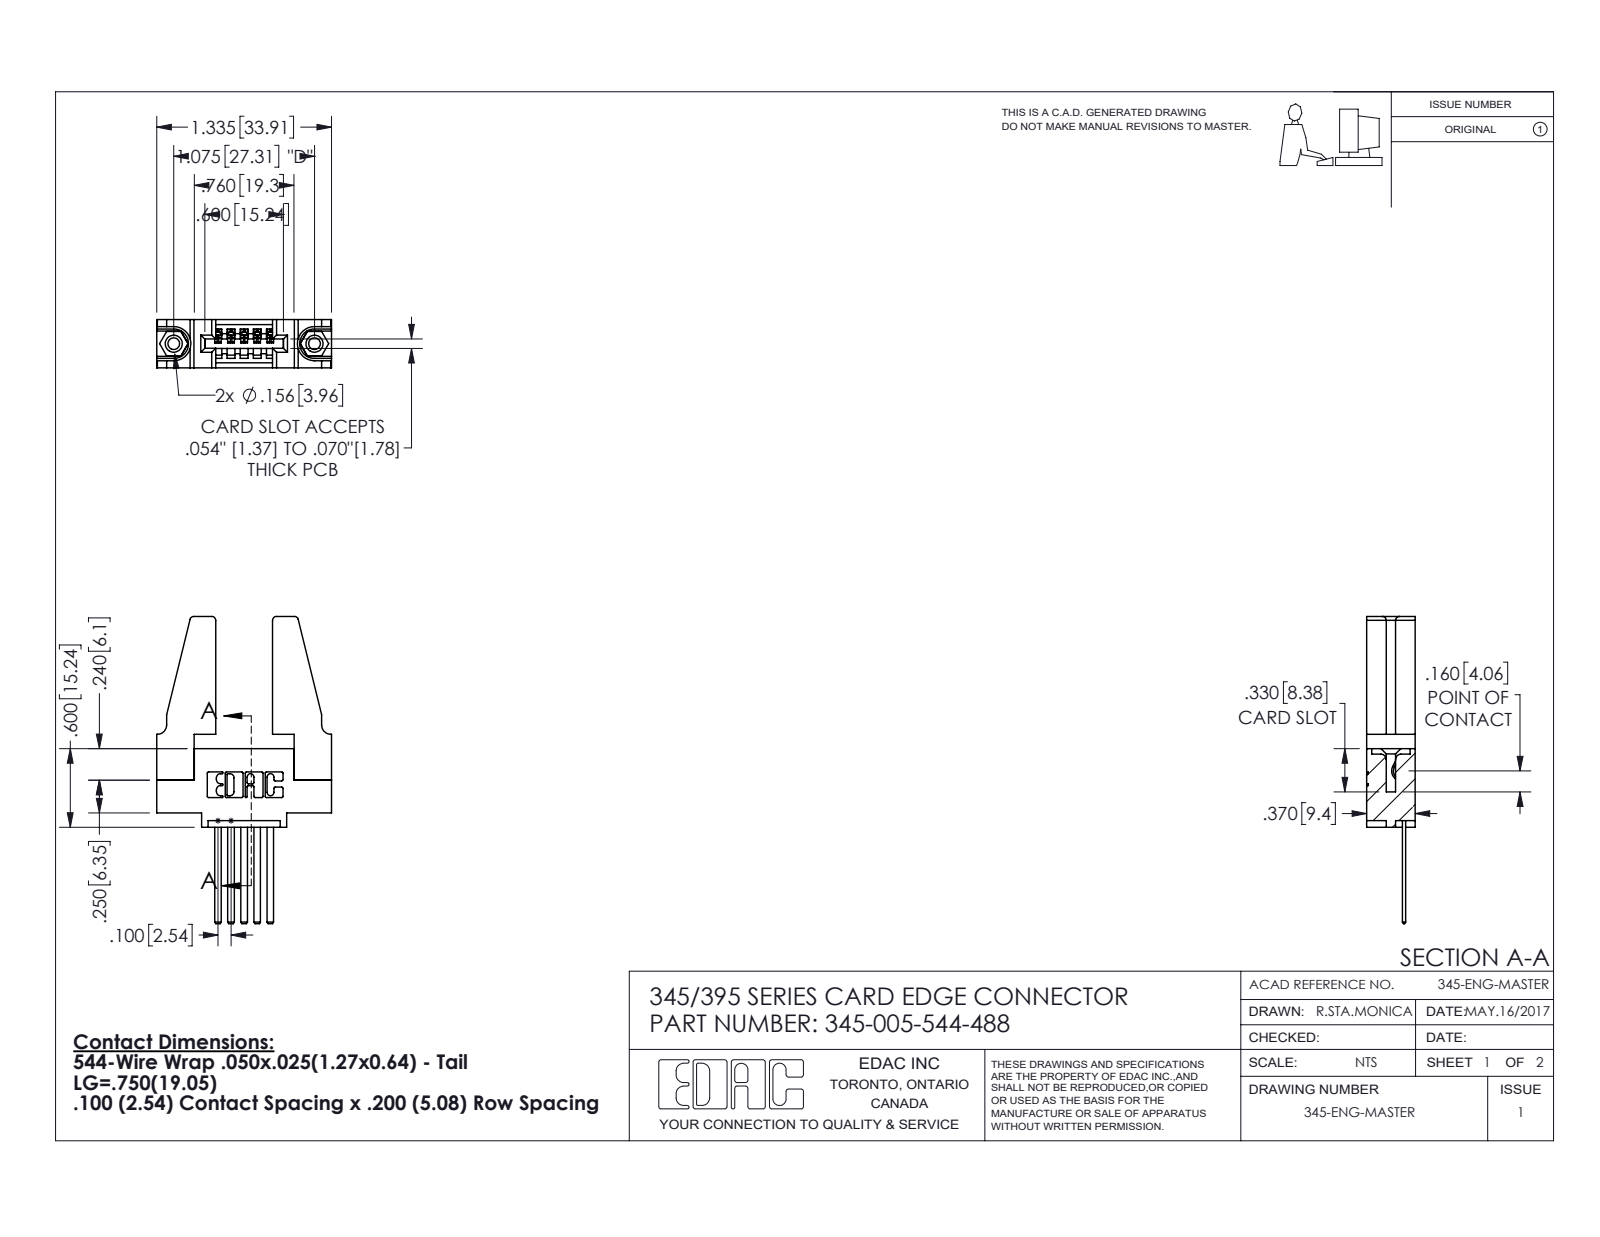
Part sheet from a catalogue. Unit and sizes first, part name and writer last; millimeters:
Units: millimetres
Overall size (bounding box): 59.6 × 33.9 × 9.4
Round holes (diameter × count): ⌀2.3 ×2, ⌀3.2 ×2, ⌀4 ×2, ⌀1.6 ×1
Round bosses / shafts (diameter × count): ⌀3.9 ×2
Partial cylindrical surfaces — rounded edges, fillets, slot ends (radius × count): R0.3 ×22, R0.2 ×10, R0.8 ×8, R0.2 ×6, R0.8 ×6, R0.7 ×3, R0.8 ×2, R1 ×2
Main face-to-face distances: 9.4, 1.8, 7.6, 5.1, 2.5, 6.9, 0.6, 3.8, 3.8, 5.6
Hole centre spacings: 6.9, 21.5, 27.3
Volume: 6 160 mm³ · Surface area: 6 742 mm²
Bodies: 10 solids, 514 faces (336 planar, 162 cylindrical, 16 other)
Part name (STEP PRODUCT): 345-250-001_345-250-001-102; 345-005-544-488; 345-292-001_345-293-144; 345-220-078_345-220-088 (+1 more)
STEP written by: SolidWorks 2016 (CONFIG_CONTROL_DESIGN)
